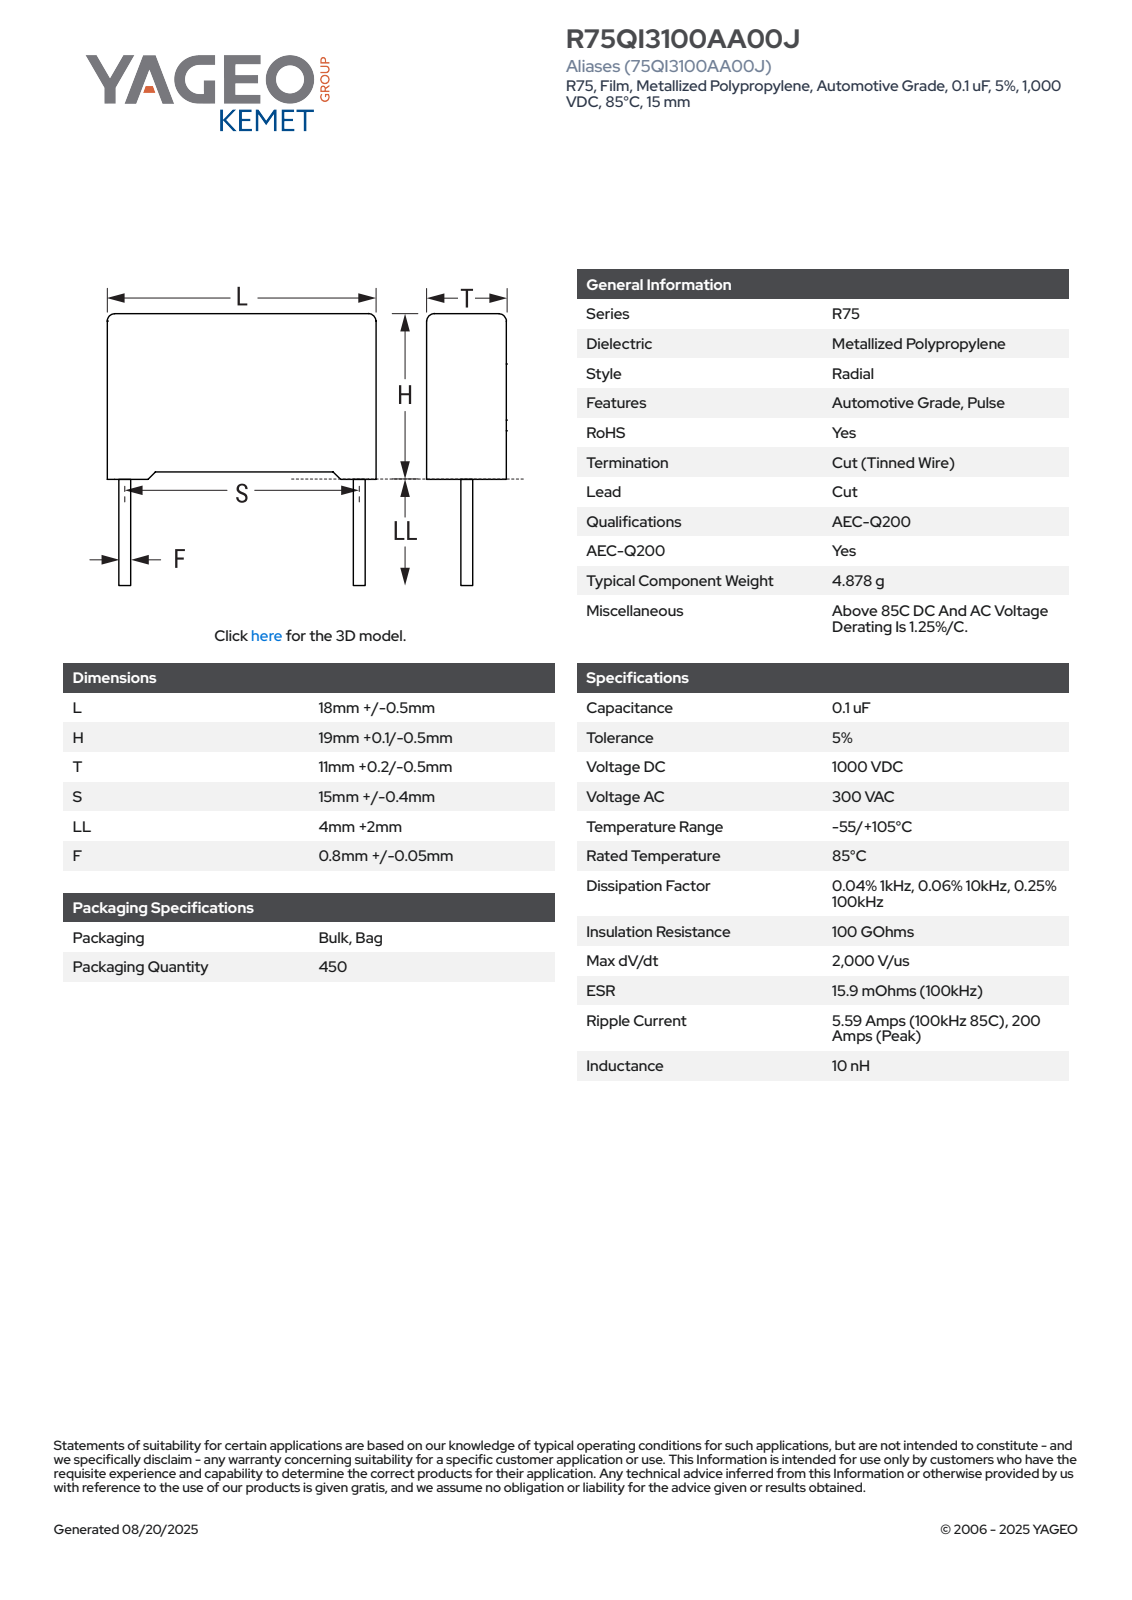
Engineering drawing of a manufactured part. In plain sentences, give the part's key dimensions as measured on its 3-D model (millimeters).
The part is named "CFR_RB2_18X19X11_L18.5H19.1T11.2S15LL6F0.85". Its 3-D file was written by "SolidWorks 2021 (AUTOMOTIVE_DESIGN)". It is 4 solids with 85 faces: 77 planar, 8 cylindrical and 0 other. Overall it measures 25.1 by 18.5 by 11.21 millimeters. Its volume is 3 824 cubic millimeters and its surface area 1 609 square millimeters. Round bosses or shafts: 2 of diameter 0.85. Partial cylindrical surfaces (rounded edges, fillets, slot ends): 4 of radius 0.5. The main face-to-face distances are 11.2, 18.5, 18.35, 0.62, 0.75, 19.1, 17.88, 0.66, 18.44, 10.58.
